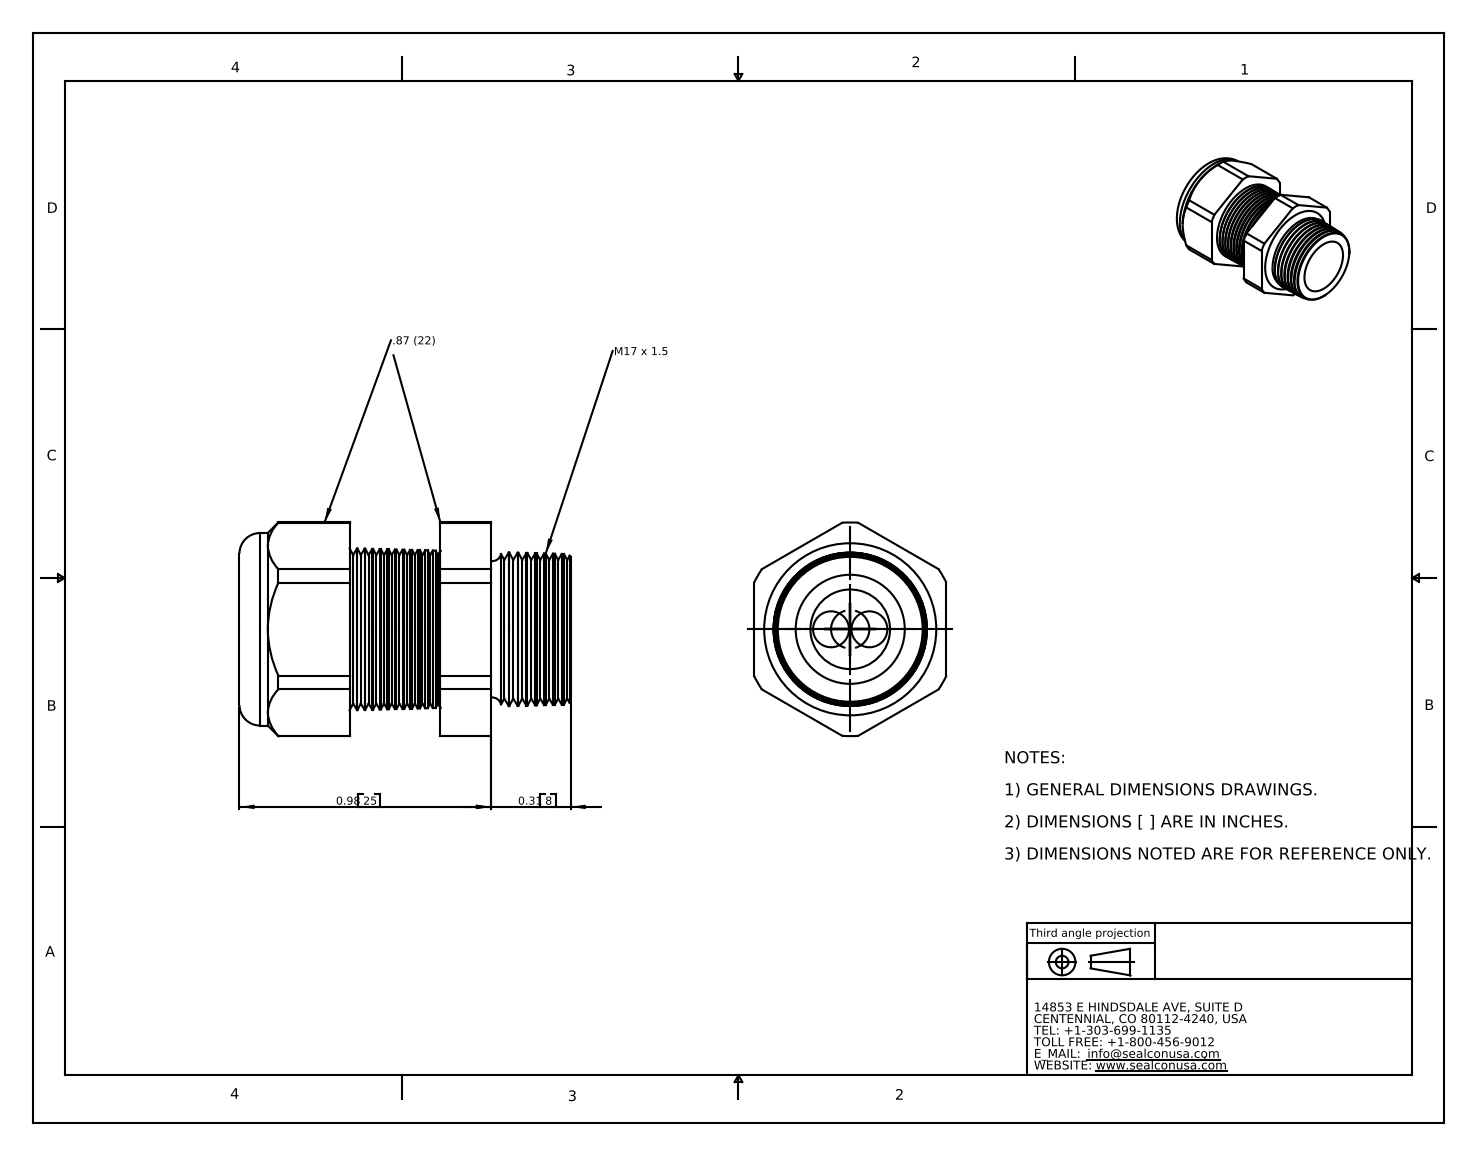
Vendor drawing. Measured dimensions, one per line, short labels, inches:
name: CD17M3-GY
written by: SolidWorks 2007 (CONFIG_CONTROL_DESIGN)
unit: in
bodies: 2 solids, 183 faces (21 planar, 24 cylindrical, 138 other)
size: 1.29 × 0.833 × 0.75
volume: 0.353 in³; area: 6.652 in²
holes: 2× ⌀0.14, 1× ⌀0.29, 1× ⌀0.31
bosses: 1× ⌀0.75
rounds: 1× R0.416
face distances: 0.75, 0.75, 0.783, 0.429, 0.354, 0.98, 0.551, 0.197, 1.29, 0.861
hole spacings: 0.075, 0.15
